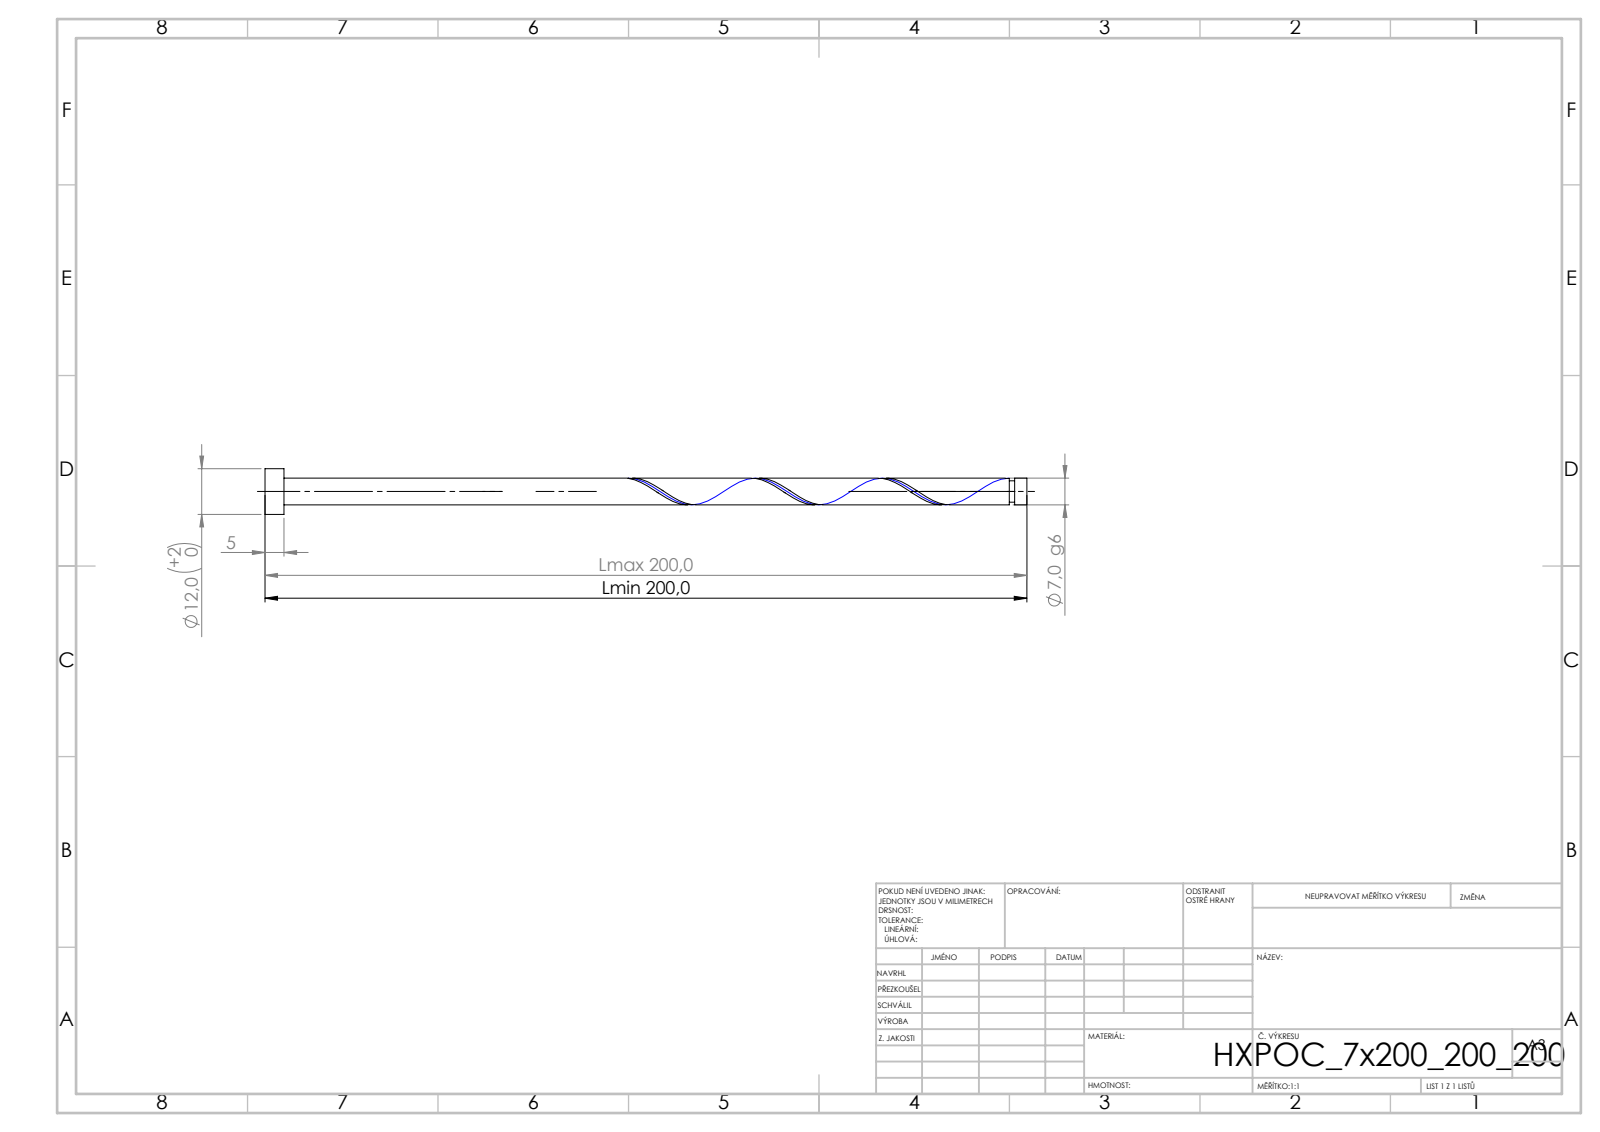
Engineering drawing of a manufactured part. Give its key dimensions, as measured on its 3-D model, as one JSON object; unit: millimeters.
{"step_written_by": "SolidWorks 2019 (CONFIG_CONTROL_DESIGN)", "units": "millimeters", "bodies": {"solids": 1, "faces": 21, "planar": 6, "cylindrical": 14, "other": 1}, "overall_size": [200, 12, 12], "volume_mm3": 7977, "surface_area_mm2": 4810, "round_bosses_or_shafts": [[12, 1], [7, 1], [5.6, 1]], "face_to_face_distances": [5, 200, 195, 196.79, 191.79, 3.21, 195.39, 190.39, 1.4, 4.61]}
